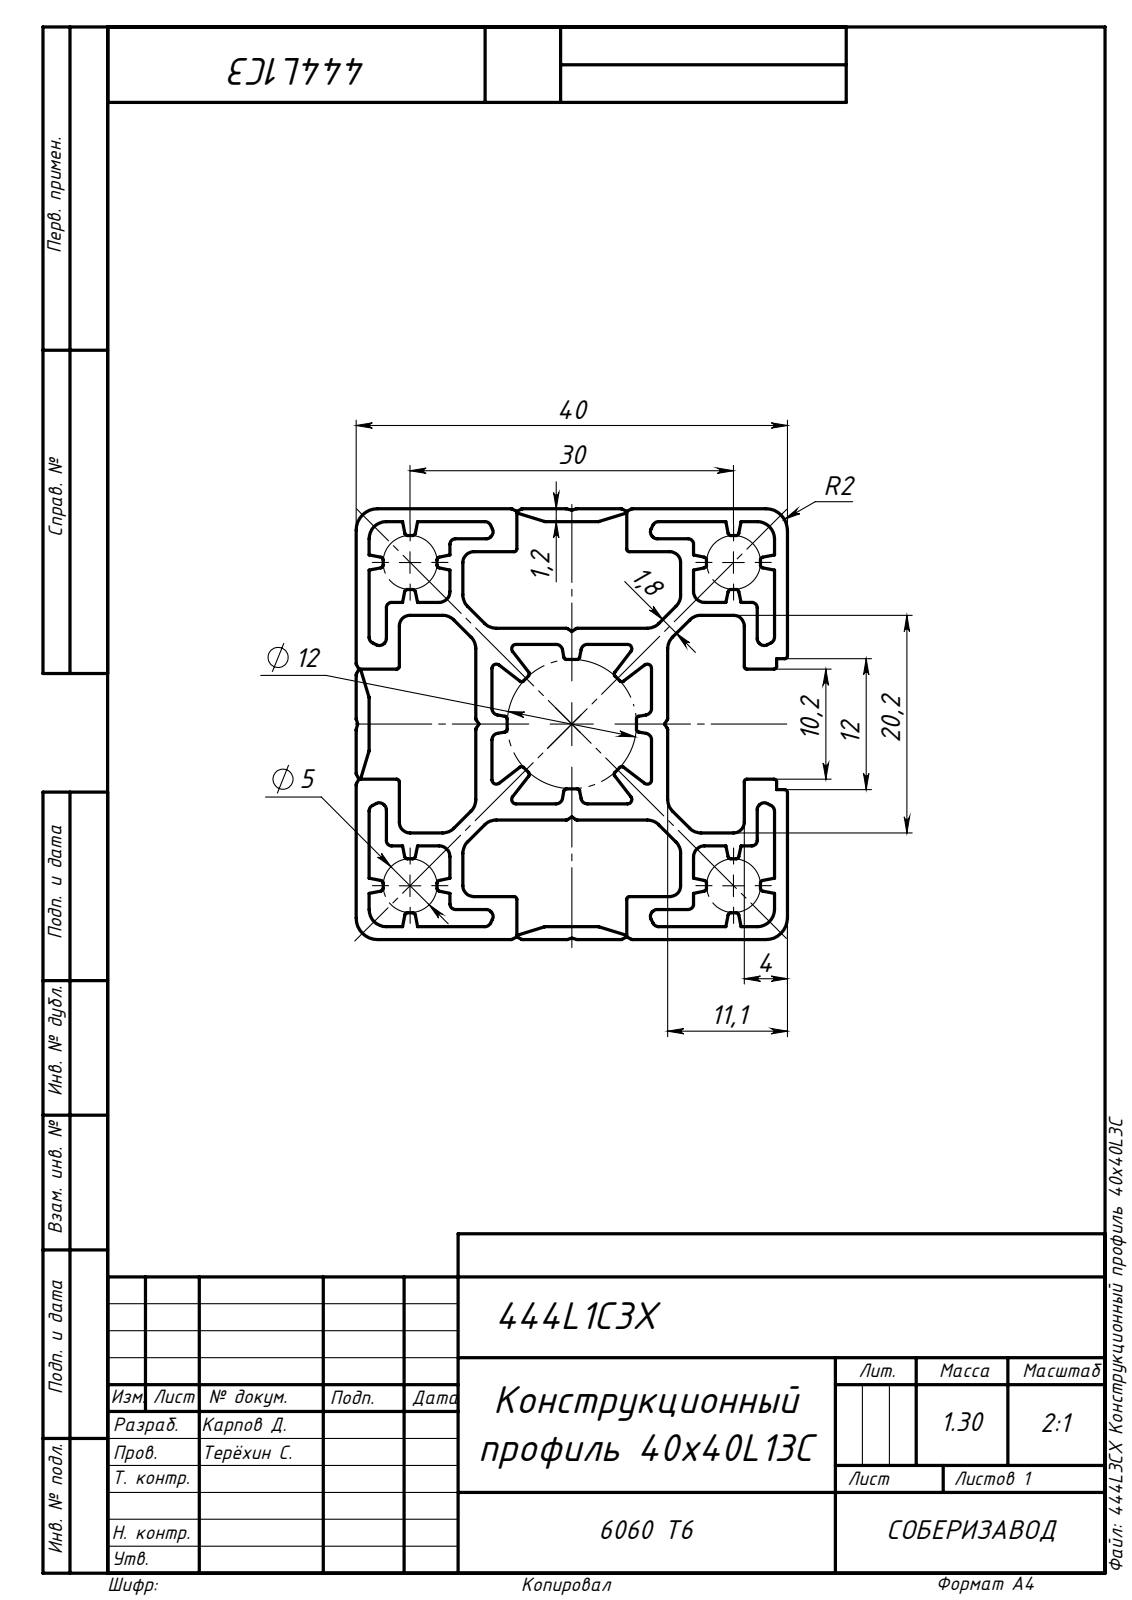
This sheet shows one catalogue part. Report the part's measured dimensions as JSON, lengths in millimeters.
{"step_written_by": "SolidWorks 2019 (AUTOMOTIVE_DESIGN)", "units": "millimeters", "bodies": {"solids": 1, "faces": 431, "planar": 231, "cylindrical": 200, "other": 0}, "overall_size": [1000, 40, 40], "volume_mm3": 481989, "surface_area_mm2": 654320, "partial_cylinders_radius": [[0.25, 92], [0.6, 32], [1.5, 16], [1, 12], [0.4, 8], [0.5, 8], [1.6, 4], [2, 4]], "face_to_face_distances": [1.2, 38.8, 9.9, 28.9, 40, 2.8, 36, 7.1, 11.1, 27.7]}
